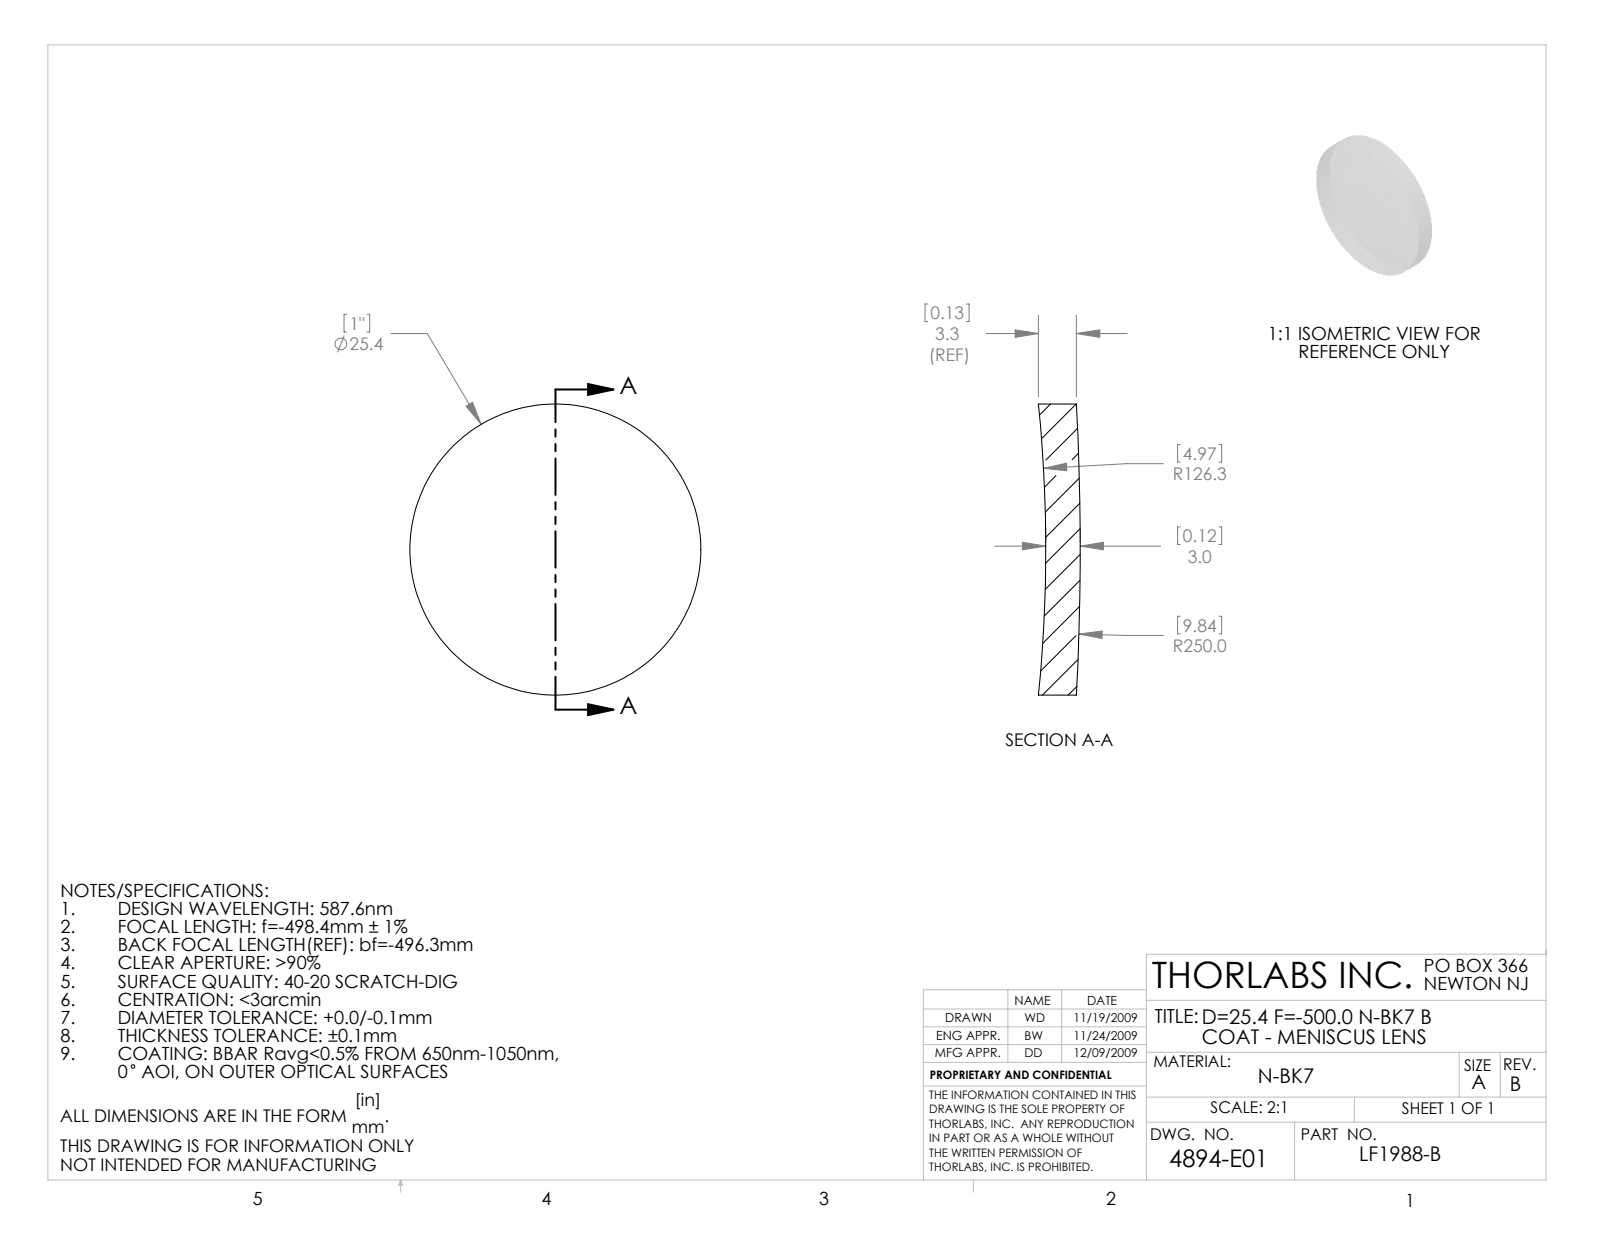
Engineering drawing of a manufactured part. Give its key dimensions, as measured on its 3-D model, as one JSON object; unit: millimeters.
{"part_name": "4894-E0W", "step_written_by": "SolidWorks 2009 (AUTOMOTIVE_DESIGN)", "units": "millimeters", "bodies": {"solids": 1, "faces": 6, "planar": 0, "cylindrical": 2, "other": 4}, "overall_size": [25.4, 25.4, 3.64], "volume_mm3": 1600, "surface_area_mm2": 1280, "round_bosses_or_shafts": [[25.4, 1]]}
